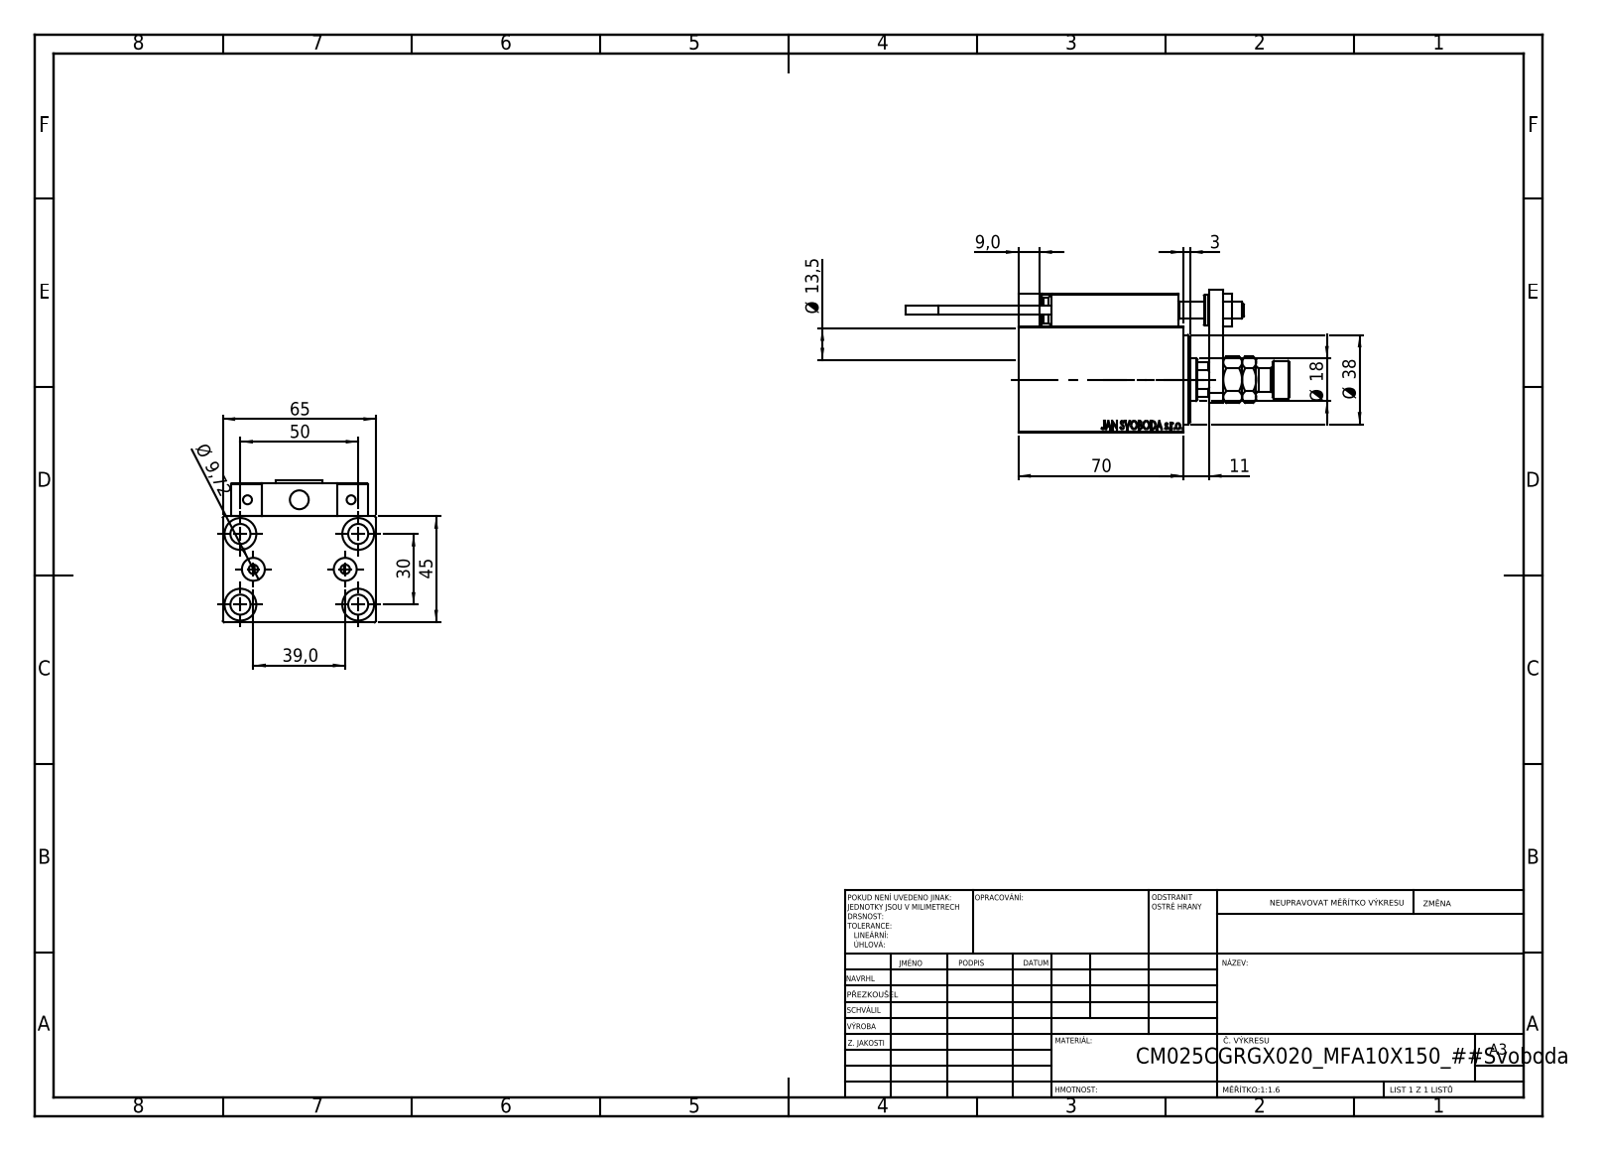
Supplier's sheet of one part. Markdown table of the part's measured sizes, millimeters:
| quantity | value |
| --- | --- |
| part name | NUT_D12; V450CM_C_Body; MAGNET; X_Y_MFA (+8 more) |
| STEP written by | SolidWorks 2019 (CONFIG_CONTROL_DESIGN) |
| units | millimeters |
| bodies | 24 solids, 1330 faces (576 planar, 188 cylindrical, 566 other) |
| overall size | 163 × 65 × 60.5 |
| volume | 229 419 mm³ |
| surface area | 72 024 mm² |
| round holes (diameter × count) | 4 × 6, 8 × 5, 8.5 × 5, 3.2 × 4, 13.5 × 4, 5 × 2, 9.72 × 2, 7 × 1, 14.5 × 1, 18 × 1, 21.5 × 1, 25 × 1 |
| round bosses / shafts (diameter × count) | 5 × 2, 3.8 × 2, 16 × 1, 13 × 1, 11 × 1, 10 × 1 |
| partial cylindrical surfaces (radius × count) | 0.3 × 30, 3 × 2, 8.5 × 1 |
| main face-to-face distances | 45, 65, 59, 14, 6, 3, 19, 5, 7, 81 |
| hole center spacings | 15.98, 29.15, 46.96, 11.37, 19.5, 20, 22.09, 28.9 |
